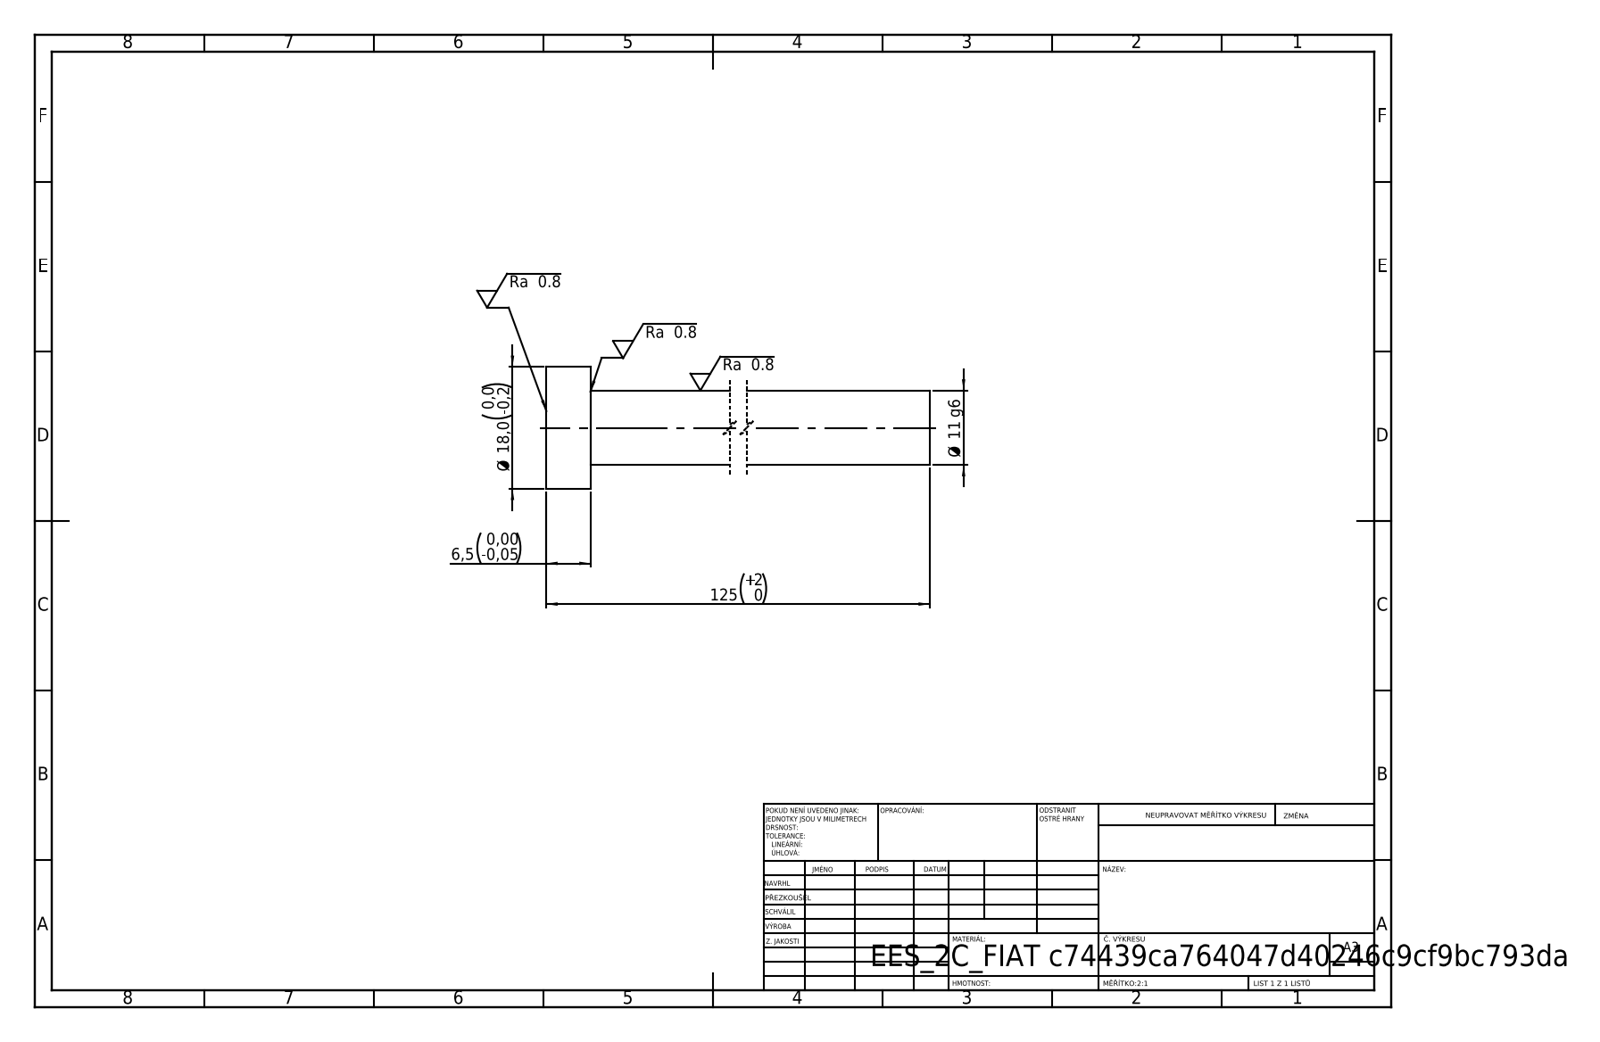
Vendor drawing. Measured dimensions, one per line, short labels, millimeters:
written by: SolidWorks 2019 (CONFIG_CONTROL_DESIGN)
unit: mm
bodies: 1 solid, 7 faces (3 planar, 4 cylindrical, 0 other)
size: 125 × 18 × 18
volume: 12 915 mm³; area: 4 972 mm²
bosses: 1× ⌀18, 1× ⌀11
face distances: 6.5, 125, 118.5
